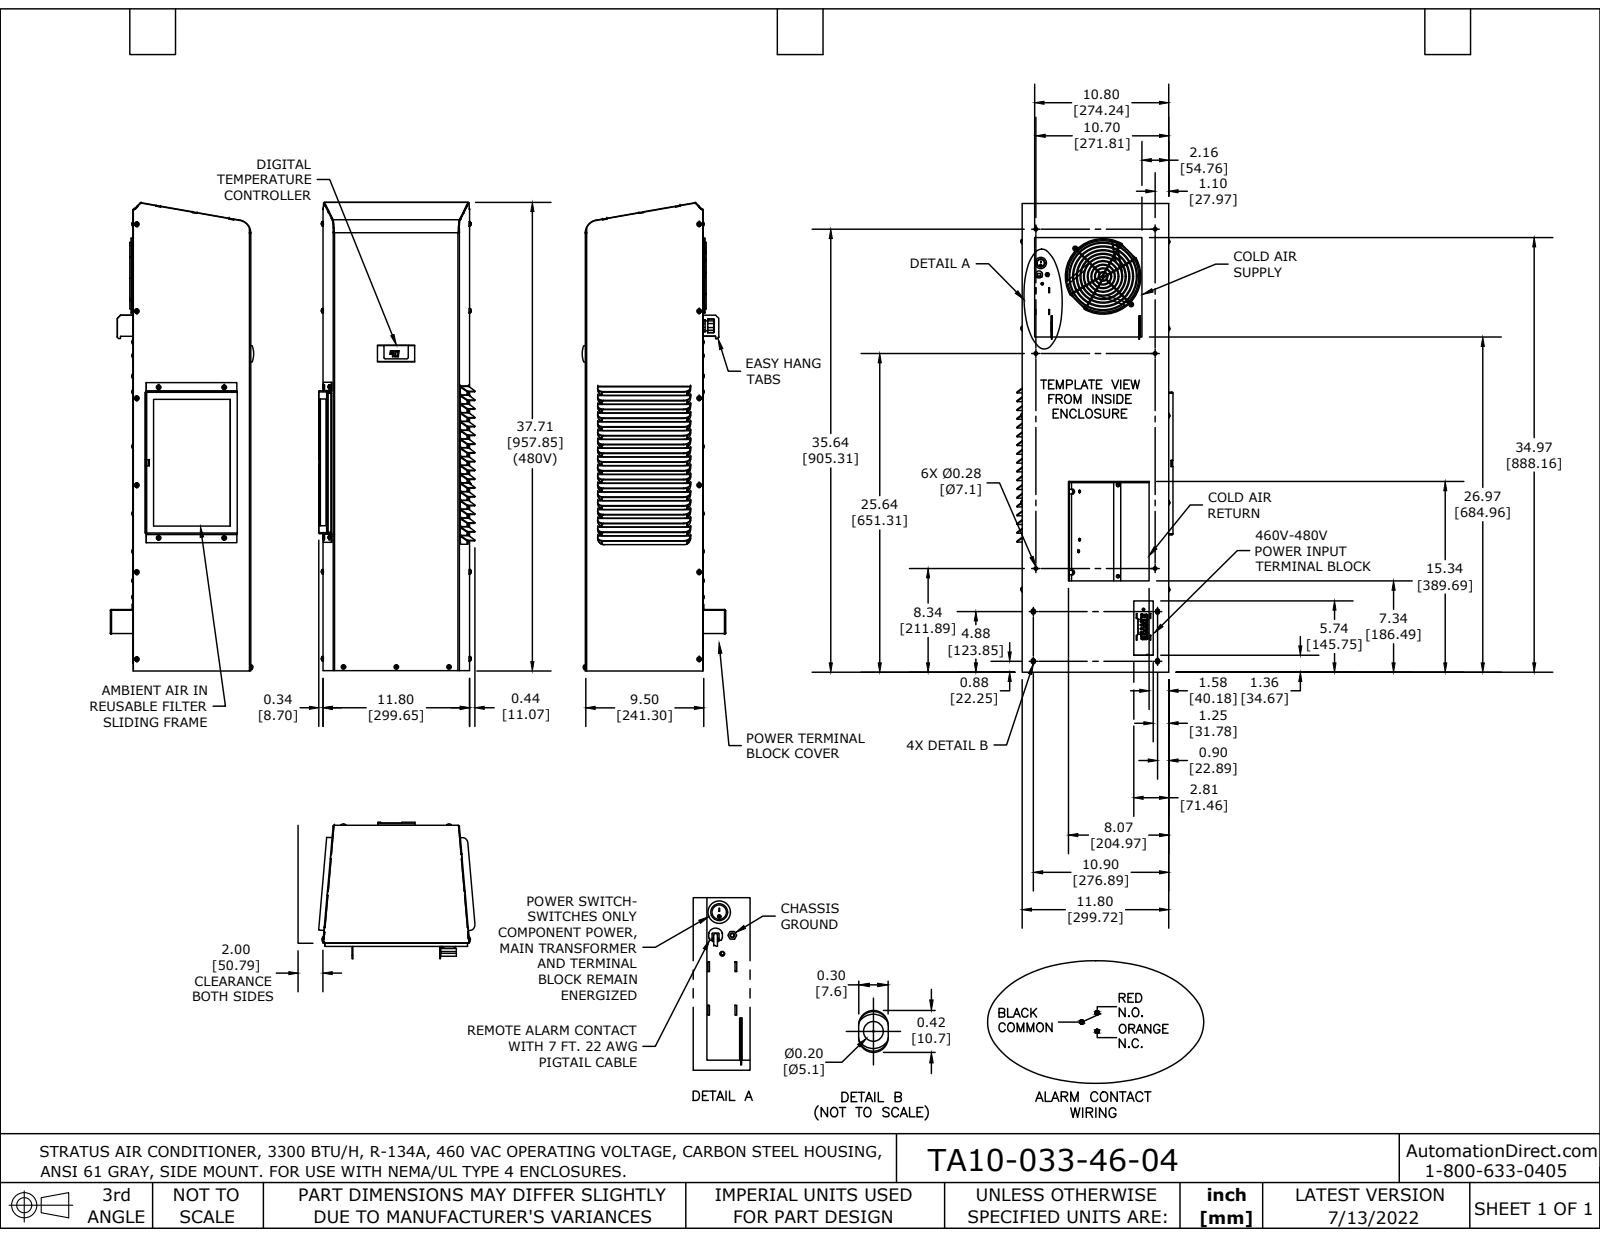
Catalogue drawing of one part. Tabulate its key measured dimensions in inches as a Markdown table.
| quantity | value |
| --- | --- |
| part name | TA10-033-46-04 |
| STEP written by | SolidWorks 2021 (AUTOMOTIVE_DESIGN) |
| units | inches |
| bodies | 1 solid, 1958 faces (1208 planar, 568 cylindrical, 182 other) |
| overall size | 32.024 × 12.576 × 11.554 |
| volume | 144.5 in³ |
| surface area | 3 631 in² |
| round holes (diameter × count) | 0.194 × 17, 0.219 × 15, 0.159 × 11, 0.204 × 5, 0.099 × 3, 0.4 × 2, 0.136 × 1, 6 × 1 |
| round bosses / shafts (diameter × count) | 0.19 × 7, 0.353 × 2, 0.248 × 2, 6.07 × 1, 0.906 × 1, 0.384 × 1, 0.375 × 1, 0.087 × 1 |
| partial cylindrical surfaces (radius × count) | 0.015 × 45, 0.01 × 42, 0.5 × 36, 0.506 × 36, 0.1 × 28, 0.058 × 21, 0.116 × 21, 0.032 × 15 |
| main face-to-face distances | 0.058, 9.377, 9.435, 9.431, 0.054, 9.489, 0.037, 0.058, 0.373, 0.254 |
| hole center spacings | 7, 14, 5.4, 7.068, 8.894, 21, 0.524, 2.861 |
